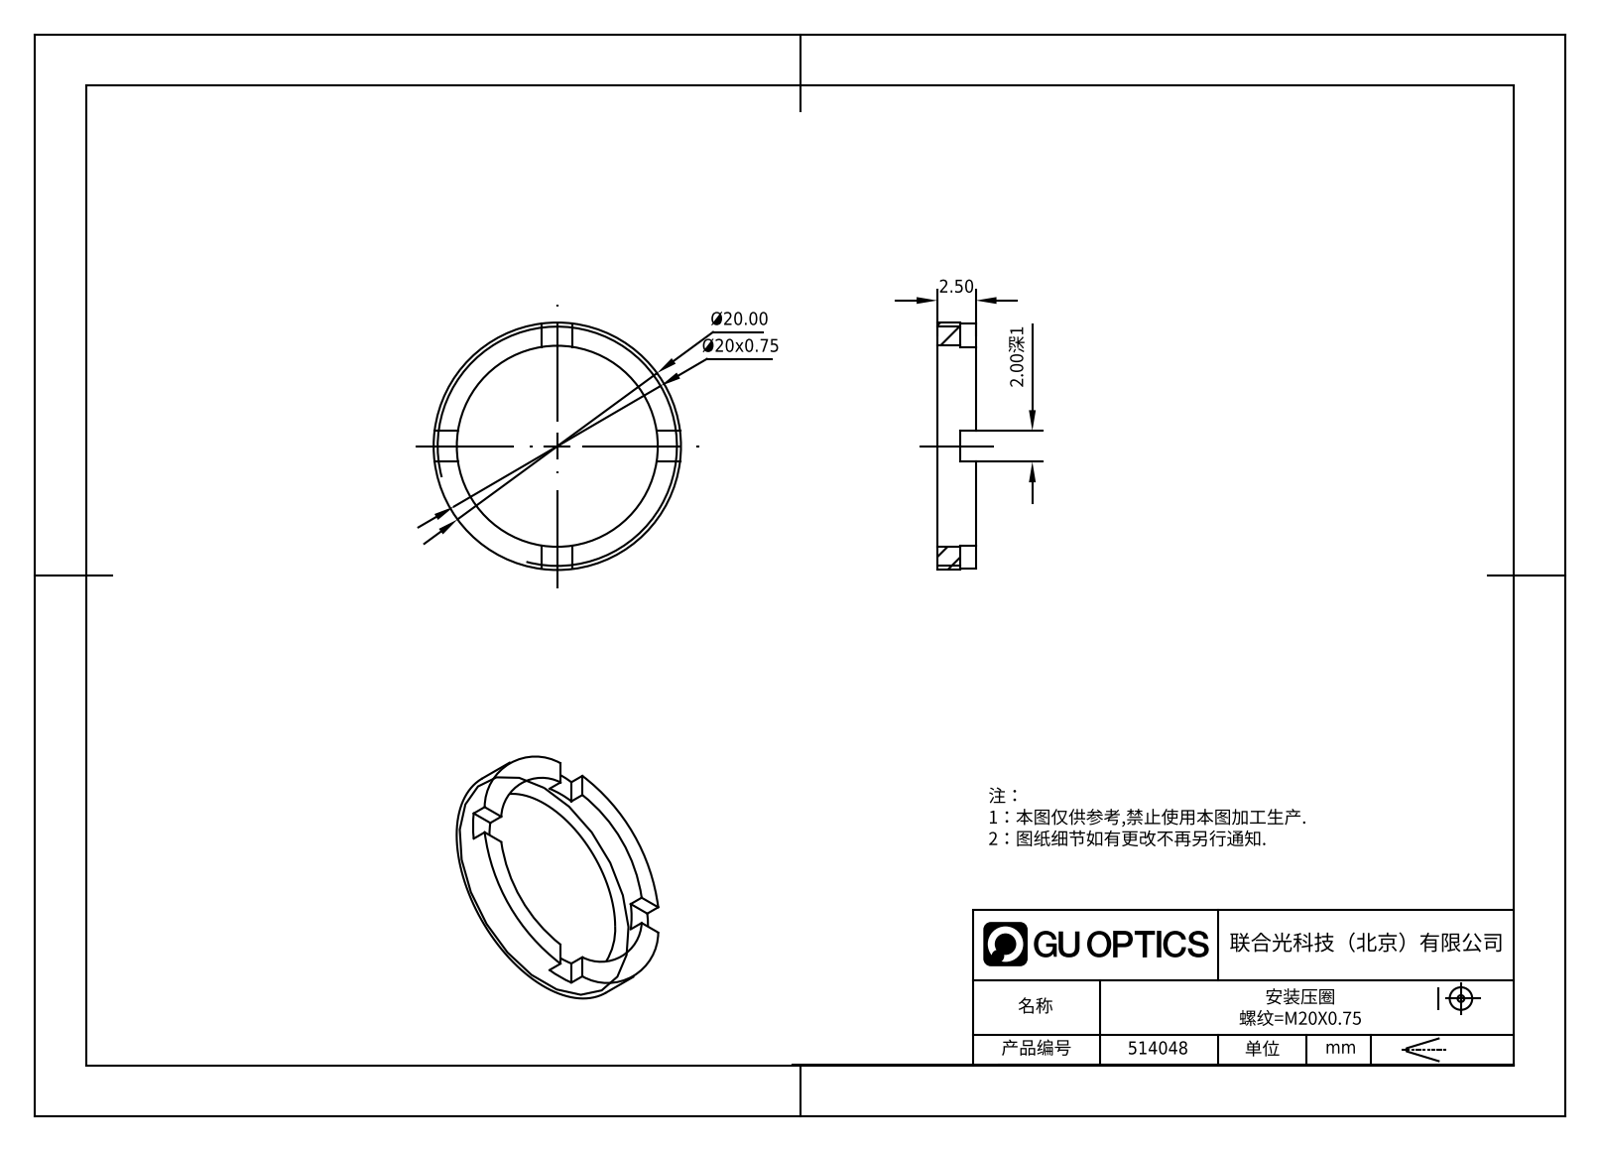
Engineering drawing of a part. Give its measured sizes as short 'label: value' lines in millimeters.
name: 514048
written by: SolidWorks 2020 (CONFIG_CONTROL_DESIGN)
unit: mm
bodies: 1 solid, 21 faces (17 planar, 4 cylindrical, 0 other)
size: 20 × 20 × 2.5
volume: 206 mm³; area: 461 mm²
holes: 1× ⌀17
bosses: 1× ⌀20
face distances: 2.5, 1.5, 1, 2
